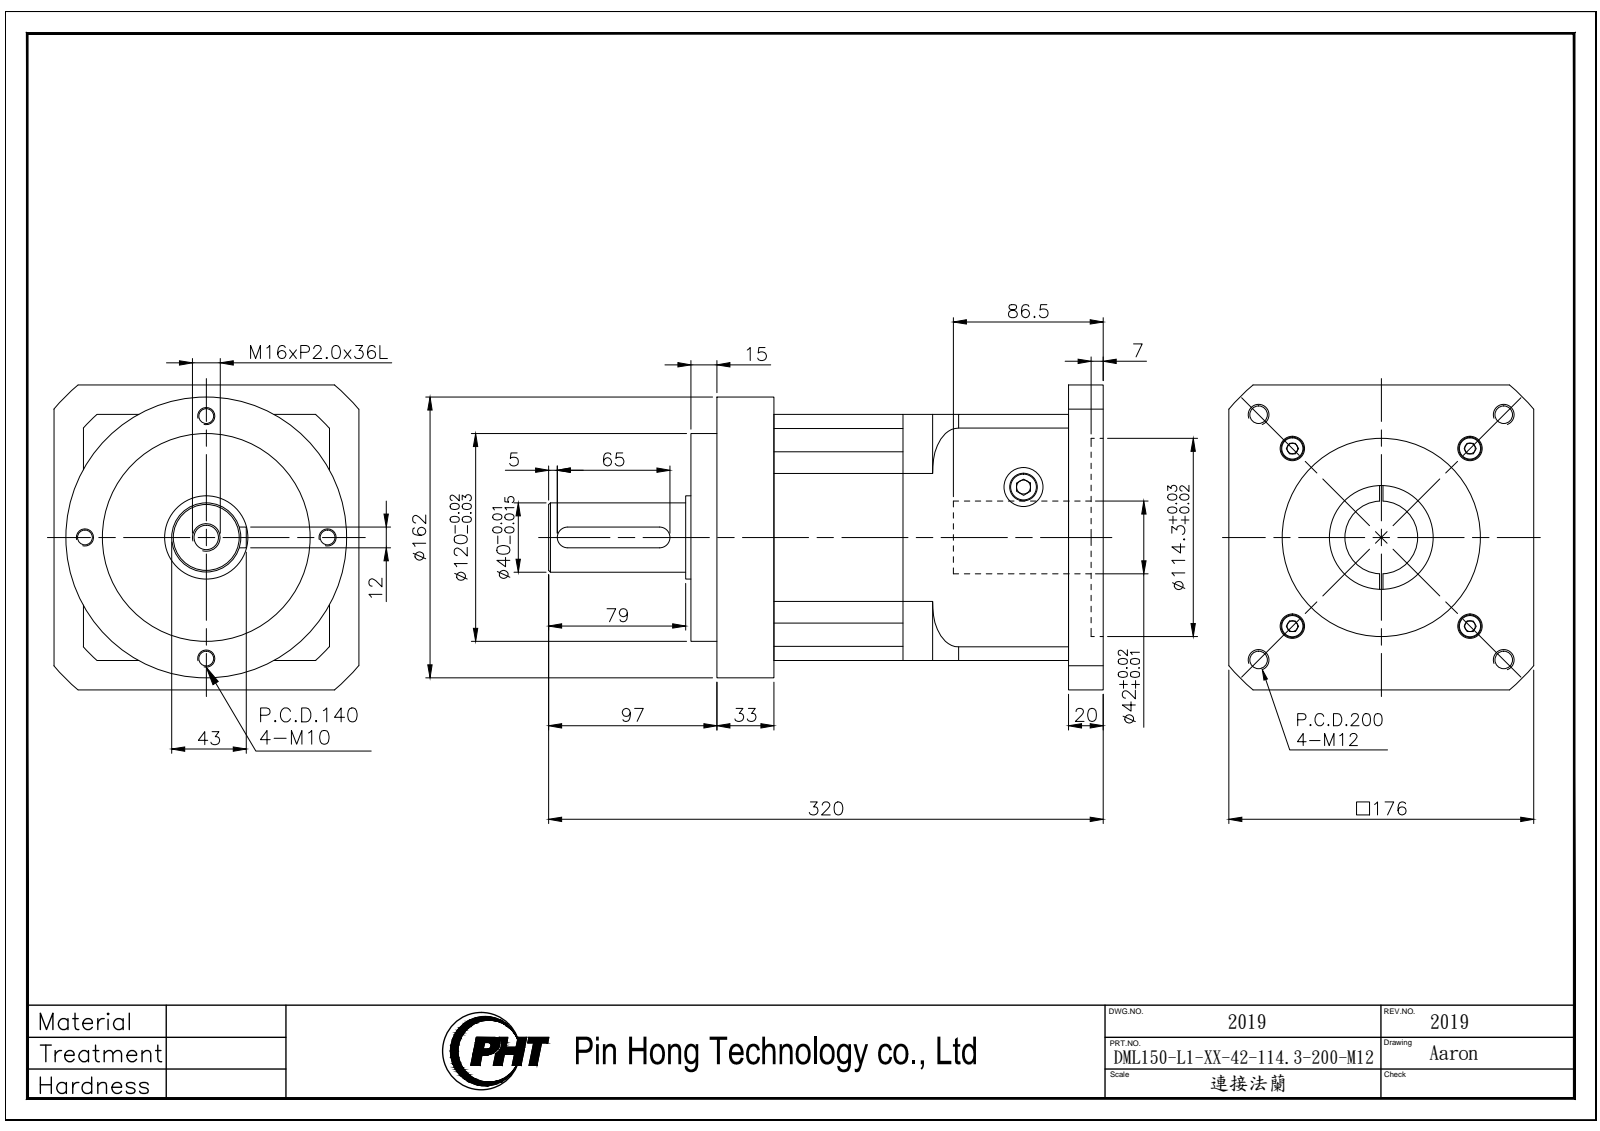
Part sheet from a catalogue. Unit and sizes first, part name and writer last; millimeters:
Units: millimetres
Overall size (bounding box): 320 × 176 × 176
Round holes (diameter × count): ⌀14 ×13, ⌀9 ×12, ⌀6.8 ×4, ⌀8.5 ×4, ⌀10.2 ×4, ⌀22.5 ×2, ⌀42 ×1, ⌀60 ×1, ⌀92 ×1, ⌀110 ×1, ⌀114.3 ×1
Round bosses / shafts (diameter × count): ⌀13 ×12, ⌀162 ×1, ⌀120 ×1, ⌀74 ×1, ⌀48 ×1, ⌀40 ×1
Partial cylindrical surfaces — rounded edges, fillets, slot ends (radius × count): R10 ×4, R6 ×2, R80 ×1, R95 ×1, R115 ×1
Main face-to-face distances: 74.5, 142, 115.5, 190, 159, 20, 17, 95.5, 170, 48
Hole centre spacings: 71, 18.79, 36.4, 36.51, 54.58, 70.51, 70.71, 87.37
Volume: 4 266 000 mm³ · Surface area: 383 054 mm²
Bodies: 3 solids, 374 faces (171 planar, 155 cylindrical, 48 other)
Part name (STEP PRODUCT): DML150-L1-XX-42-114.3-200-M12_2019
STEP written by: SolidWorks 2016 (AUTOMOTIVE_DESIGN)
